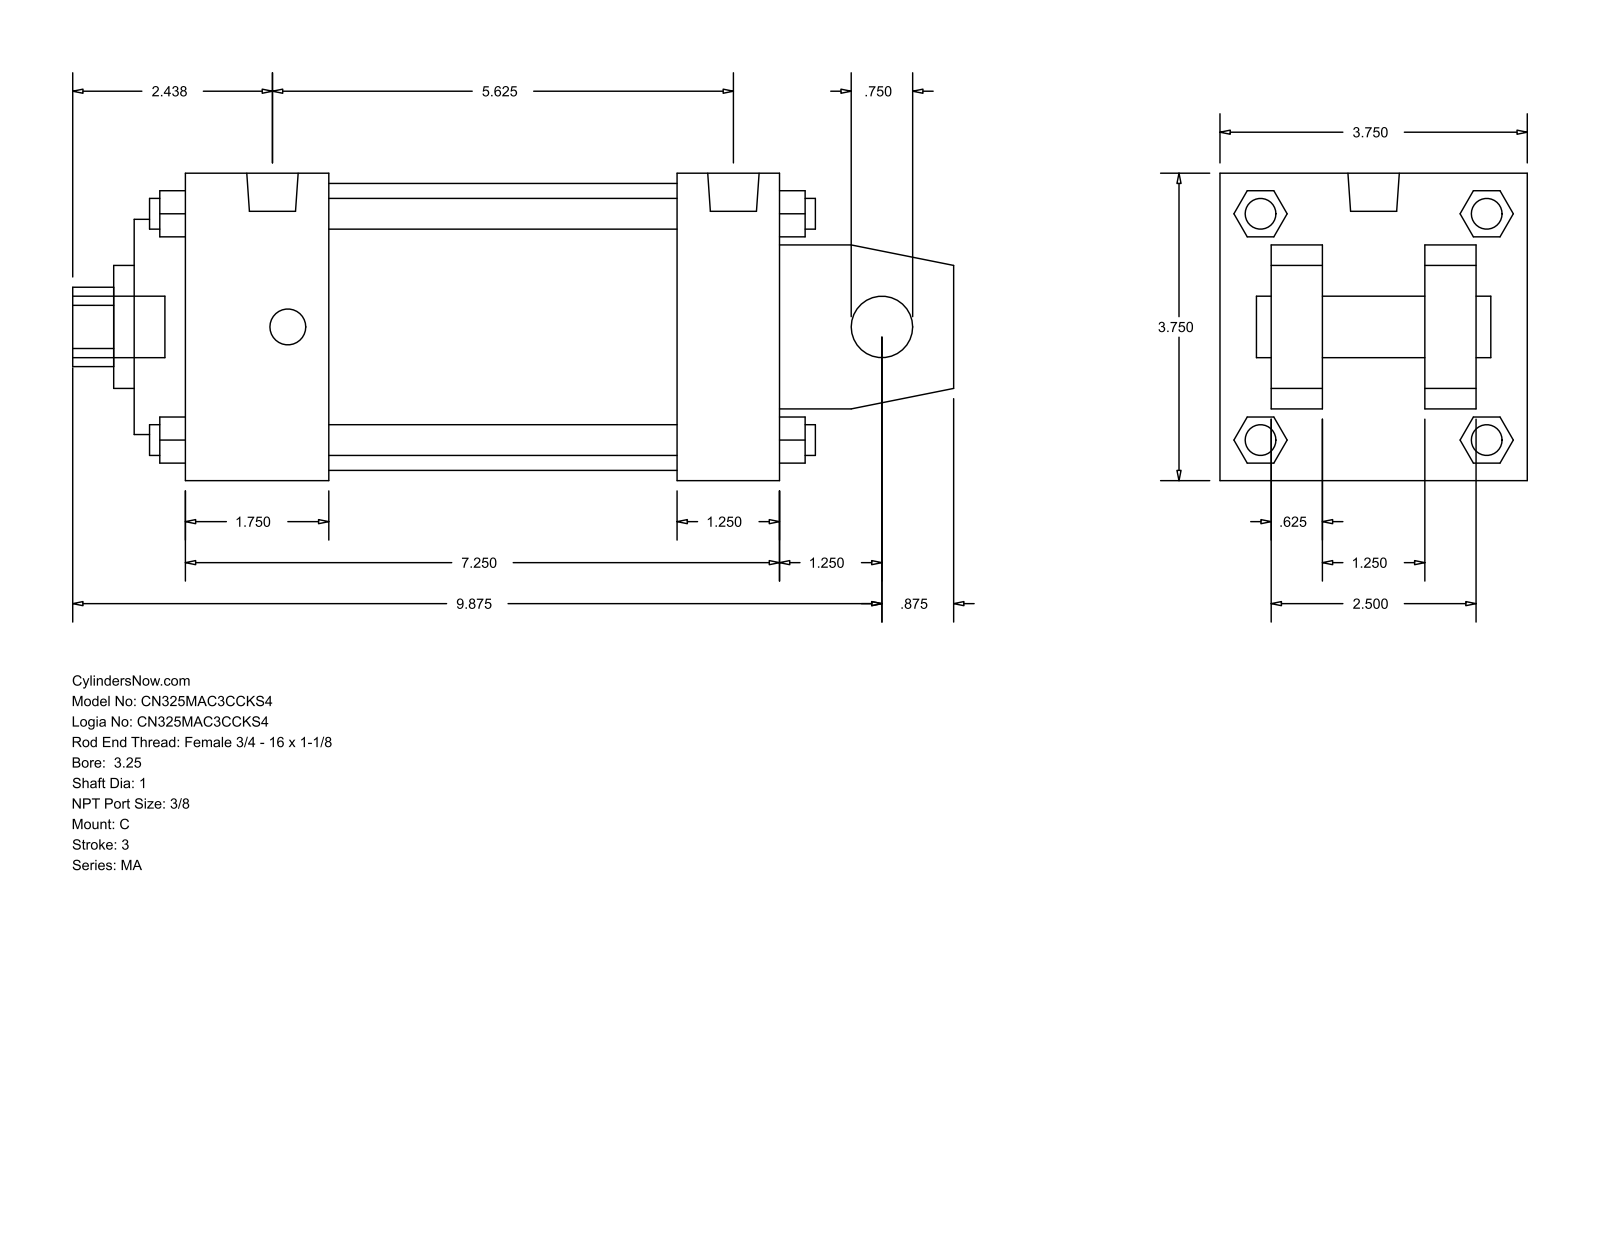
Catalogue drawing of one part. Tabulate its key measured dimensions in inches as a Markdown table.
| quantity | value |
| --- | --- |
| part name | MA_C__0325_1 |
| STEP written by | GSSL Pune (CONFIG_CONTROL_DESIGN) |
| units | inches |
| bodies | 0 solids, 141 faces (109 planar, 32 cylindrical, 0 other) |
| overall size | 10.75 × 3.75 × 3.75 |
| round holes (diameter × count) | 0.75 × 1, 1 × 1, 1.5 × 1, 2.625 × 1, 3.5 × 1 |
| round bosses / shafts (diameter × count) | 0.437 × 4, 0.375 × 4, 0.627 × 2, 0.75 × 1 |
| partial cylindrical surfaces (radius × count) | 0.484 × 1 |
| main face-to-face distances | 3.75, 0.625, 2.5, 7.25, 1.25, 3.125, 1.875, 7.875, 6, 1.25 |
